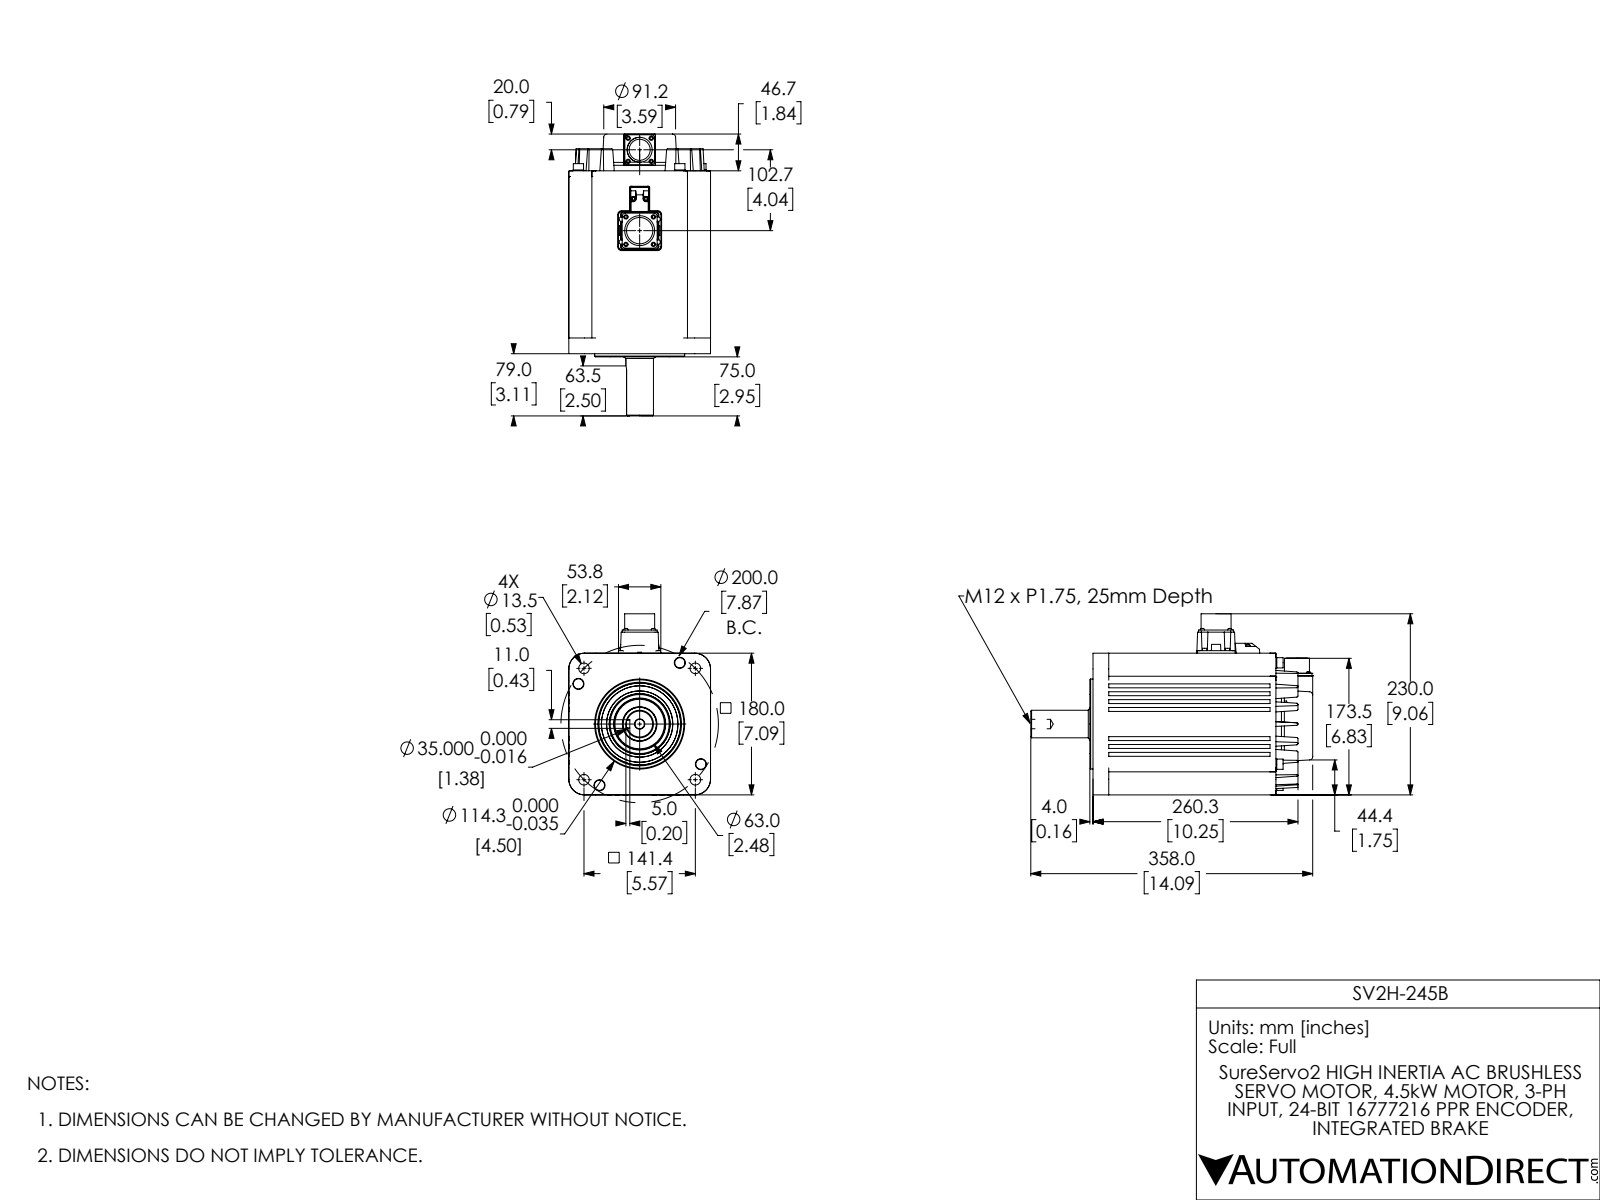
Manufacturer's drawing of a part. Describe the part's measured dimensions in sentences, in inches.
The part is named "SV2H-245B Raw Coord fXT". Its 3-D file was written by "SolidWorks 2017 (AUTOMOTIVE_DESIGN)". It is 1 solid with 635 faces: 336 planar, 204 cylindrical and 95 other. Overall it measures 14.095 by 9.056 by 7.087 inches. Its volume is 442.2 cubic inches and its surface area 556.7 square inches. Round holes: 4 of diameter 0.531, 4 of diameter 0.551, 1 of diameter 0.472, 1 of diameter 1.058, 1 of diameter 1.317, 1 of diameter 2.48. Round bosses or shafts: 7 of diameter 0.217, 4 of diameter 0.528, 4 of diameter 0.512, 4 of diameter 0.315, 2 of diameter 0.236, 1 of diameter 4.567, 1 of diameter 4.5, 1 of diameter 1.732. Partial cylindrical surfaces (rounded edges, fillets, slot ends): 17 of radius 0.197, 16 of radius 0.064, 16 of radius 0.157, 12 of radius 0.039, 4 of radius 0.02, 4 of radius 0.191, 4 of radius 0.394, 4 of radius 0.787. The main face-to-face distances are 0.197, 7.087, 0.394, 1.154, 5.933, 0.591, 3.031, 3.228, 2.835, 0.787. The hole center spacings are 0.824, 3.661, 3.937, 4.8, 5.178, 5.568, 5.897, 7.559.
